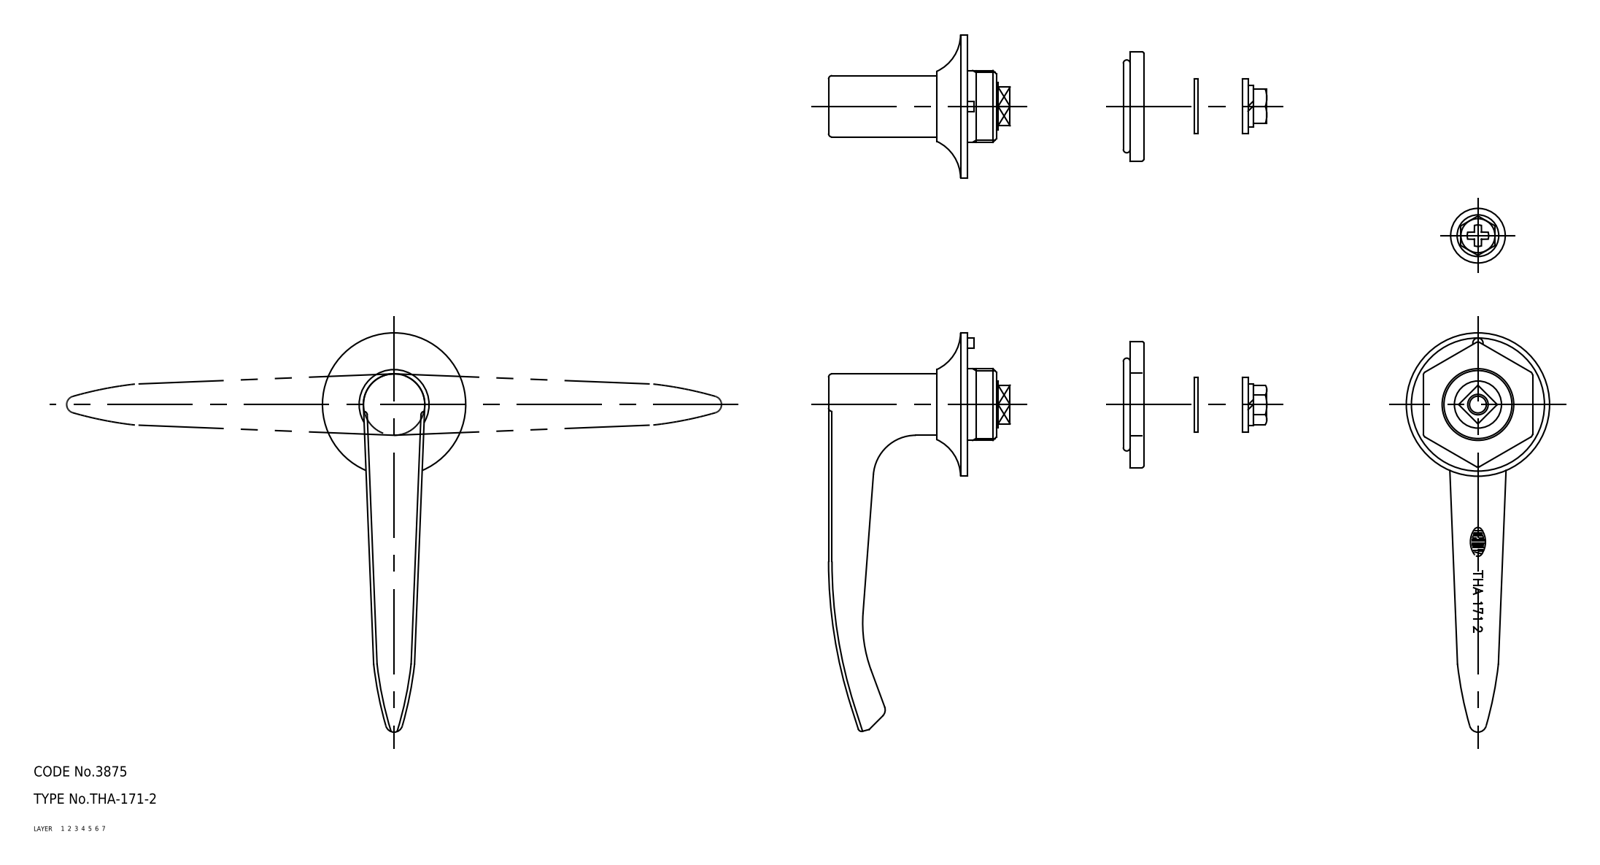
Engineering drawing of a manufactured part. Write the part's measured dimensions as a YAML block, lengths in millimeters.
part_name: "washer_A; nut; handle; bolt (+2 more)"
step_written_by: "CADfix (AUTOMOTIVE_DESIGN)"
units: millimeters
bodies: {solids: 5, faces: 170, planar: 0, cylindrical: 0, other: 170}
overall_size: [117, 60.3, 42]
volume: 33721
surface_area: 14644
